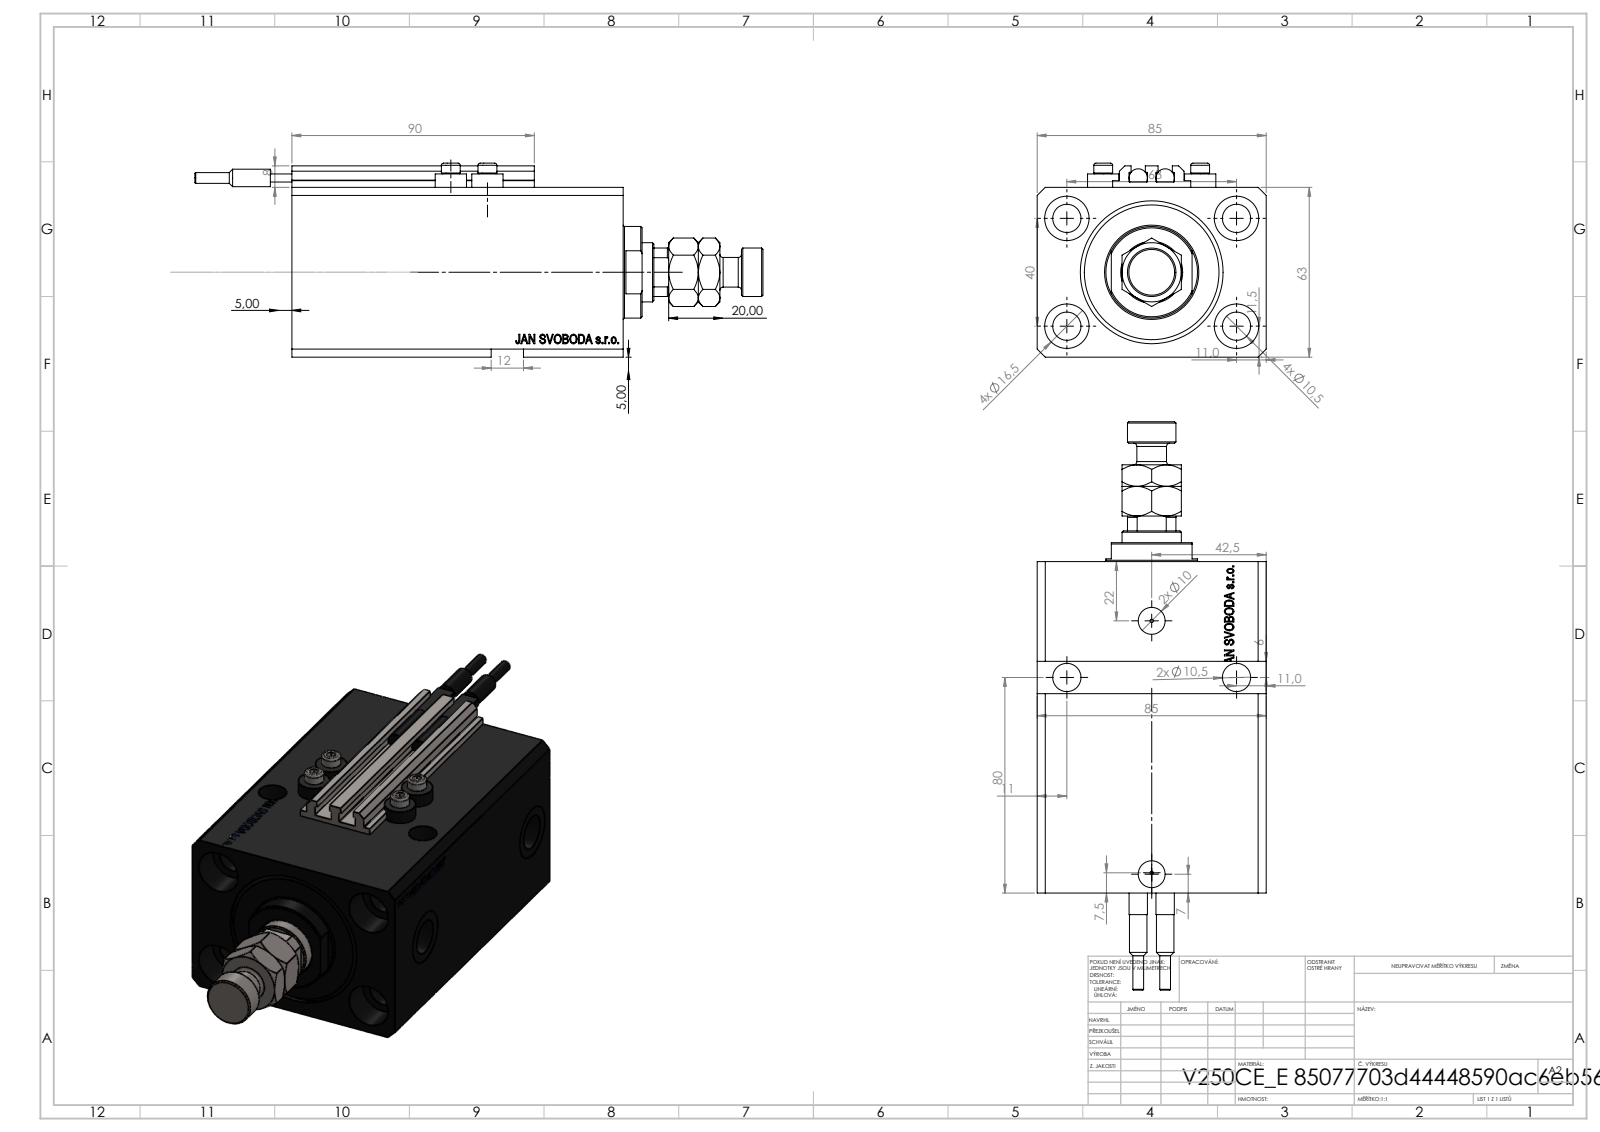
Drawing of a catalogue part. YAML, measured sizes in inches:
part_name: "SWITCH_V250CE; V250CE_VC_E; V250CE_E_Body; V250CE_C_VCP (+2 more)"
step_written_by: "SolidWorks 2019 (CONFIG_CONTROL_DESIGN)"
units: inches
bodies: {solids: 11, faces: 1211, planar: 583, cylindrical: 162, other: 466}
overall_size: [8.307, 3.346, 2.835]
volume: 34.84
surface_area: 194.2
round_holes:
  - {diameter: 0.413, count: 8}
  - {diameter: 0.049, count: 4}
  - {diameter: 0.157, count: 4}
  - {diameter: 0.65, count: 4}
  - {diameter: 0.394, count: 2}
  - {diameter: 0.518, count: 2}
  - {diameter: 0.787, count: 2}
  - {diameter: 0.492, count: 1}
  - {diameter: 0.866, count: 1}
  - {diameter: 1.575, count: 1}
  - {diameter: 2.087, count: 1}
round_bosses_or_shafts:
  - {diameter: 0.457, count: 4}
  - {diameter: 0.276, count: 4}
  - {diameter: 0.268, count: 2}
  - {diameter: 0.256, count: 2}
  - {diameter: 0.157, count: 2}
  - {diameter: 1.339, count: 1}
  - {diameter: 0.709, count: 1}
  - {diameter: 0.433, count: 1}
partial_cylinders:
  - {radius: 0.008, count: 10}
  - {radius: 0.413, count: 1}
face_to_face_distances: [2.48, 3.346, 0.669, 4.843, 4.173, 0.118, 0.449, 3.724, 4.394, 2.559]
hole_center_spacings: [1.469, 2.48, 0.535, 0.606, 0.983, 1.084, 1.324, 1.417]
